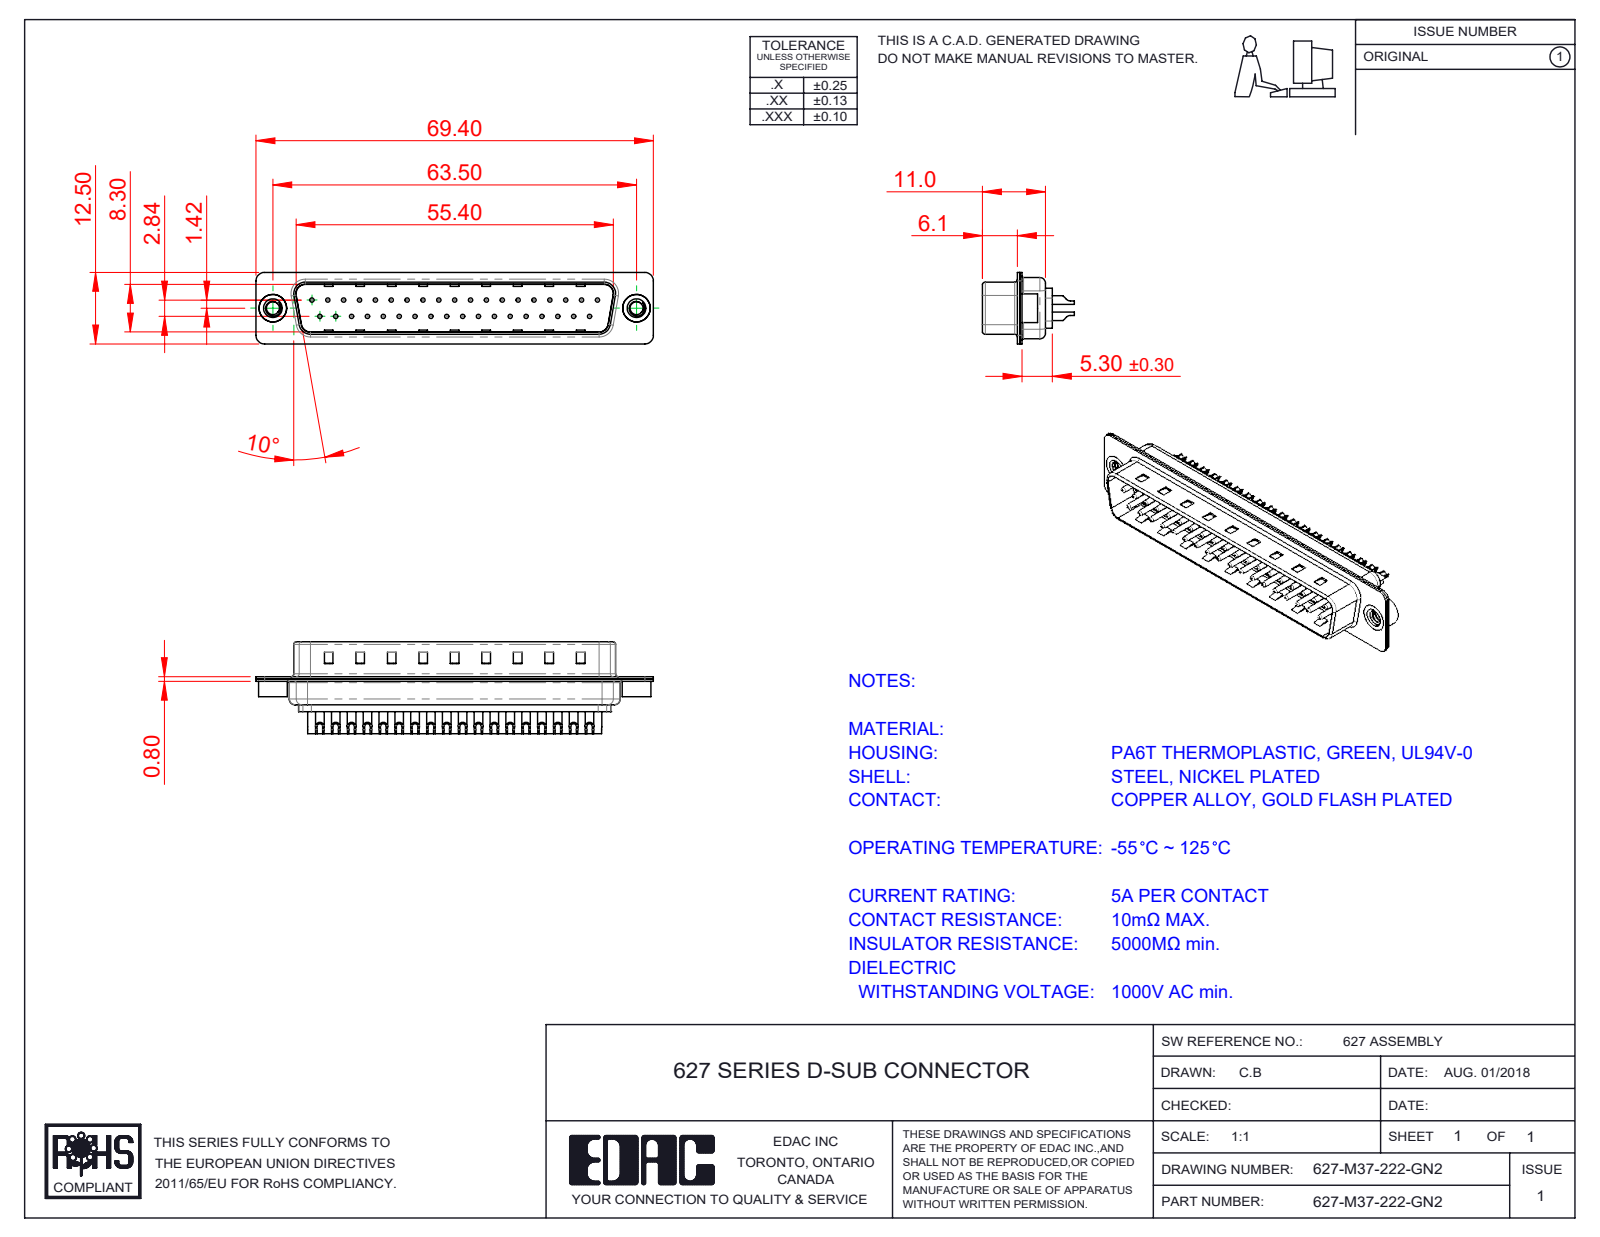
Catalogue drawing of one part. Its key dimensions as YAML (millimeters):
part_name: "627M Shell Rear_37 Contacts; 627M Housing_37 Contacts; 627M Shell Front_37 Contacts; 627M Contact Row 2_22 (+3 more)"
step_written_by: "SolidWorks 2020 (CONFIG_CONTROL_DESIGN)"
units: millimeters
bodies: {solids: 42, faces: 1781, planar: 536, cylindrical: 733, other: 512}
overall_size: [69.4, 16.05, 12.5]
volume: 3853
surface_area: 9616
round_holes:
  - {diameter: 0.75, count: 37}
  - {diameter: 1, count: 37}
  - {diameter: 1.6, count: 37}
  - {diameter: 2, count: 37}
  - {diameter: 2.26, count: 2}
  - {diameter: 4, count: 2}
  - {diameter: 4.8, count: 2}
round_bosses_or_shafts:
  - {diameter: 1.5, count: 37}
  - {diameter: 5, count: 2}
  - {diameter: 4.9, count: 2}
partial_cylinders:
  - {radius: 1.5, count: 16}
  - {radius: 2, count: 12}
  - {radius: 0.5, count: 8}
  - {radius: 1.6, count: 8}
  - {radius: 1, count: 6}
  - {radius: 0.25, count: 4}
  - {radius: 0.6, count: 4}
  - {radius: 0.65, count: 4}
face_to_face_distances: [0.4, 0.8, 9.5, 9.1, 8.7, 9.9, 1.2, 0.75, 0.35, 5.7]
hole_center_spacings: [2.77, 5.54, 3.16, 8.31, 11.08, 13.85, 16.62, 19.39]
